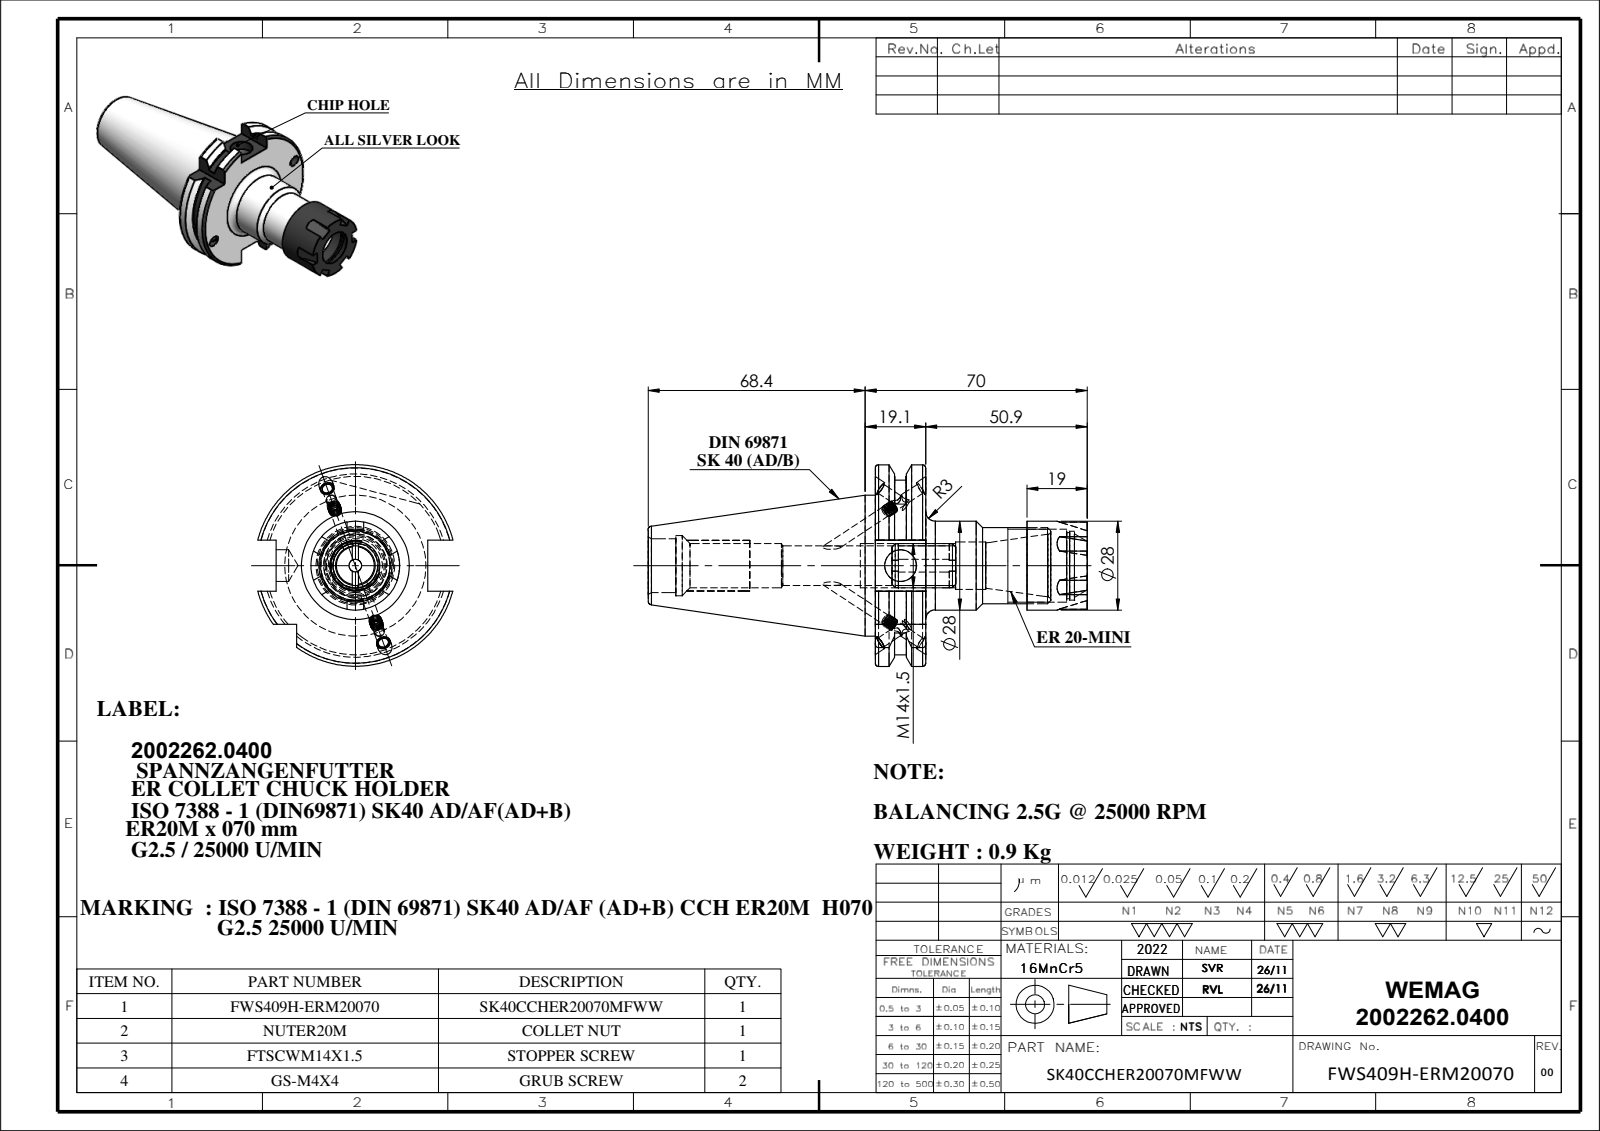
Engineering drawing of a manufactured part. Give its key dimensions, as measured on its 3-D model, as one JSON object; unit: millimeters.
{"part_name": "91406-ERM720070; SCWM14X1.5; SK40CCHER20070FWW; NUTER20M (+2 more)", "step_written_by": "SolidWorks 2018 (CONFIG_CONTROL_DESIGN)", "units": "millimeters", "bodies": {"solids": 5, "faces": 269, "planar": 87, "cylindrical": 78, "other": 104}, "overall_size": [138.4, 63.55, 61.48], "volume_mm3": 119325, "surface_area_mm2": 31570, "round_holes": [[3.3, 4], [4.5, 4], [4, 1], [10, 1], [12.5, 1], [14, 1], [15, 1], [17, 1], [19, 1], [20.8, 1], [21.76, 1], [23, 1]], "round_bosses_or_shafts": [[4, 2], [44.45, 1], [28, 1], [24, 1]], "partial_cylinders_radius": [[28.12, 1], [31.77, 1]], "face_to_face_distances": [15.9, 47.8, 66.8, 50.9, 31.9, 19, 16.1, 6.5, 25.3, 9.4], "hole_center_spacings": [35.11, 1.3]}
